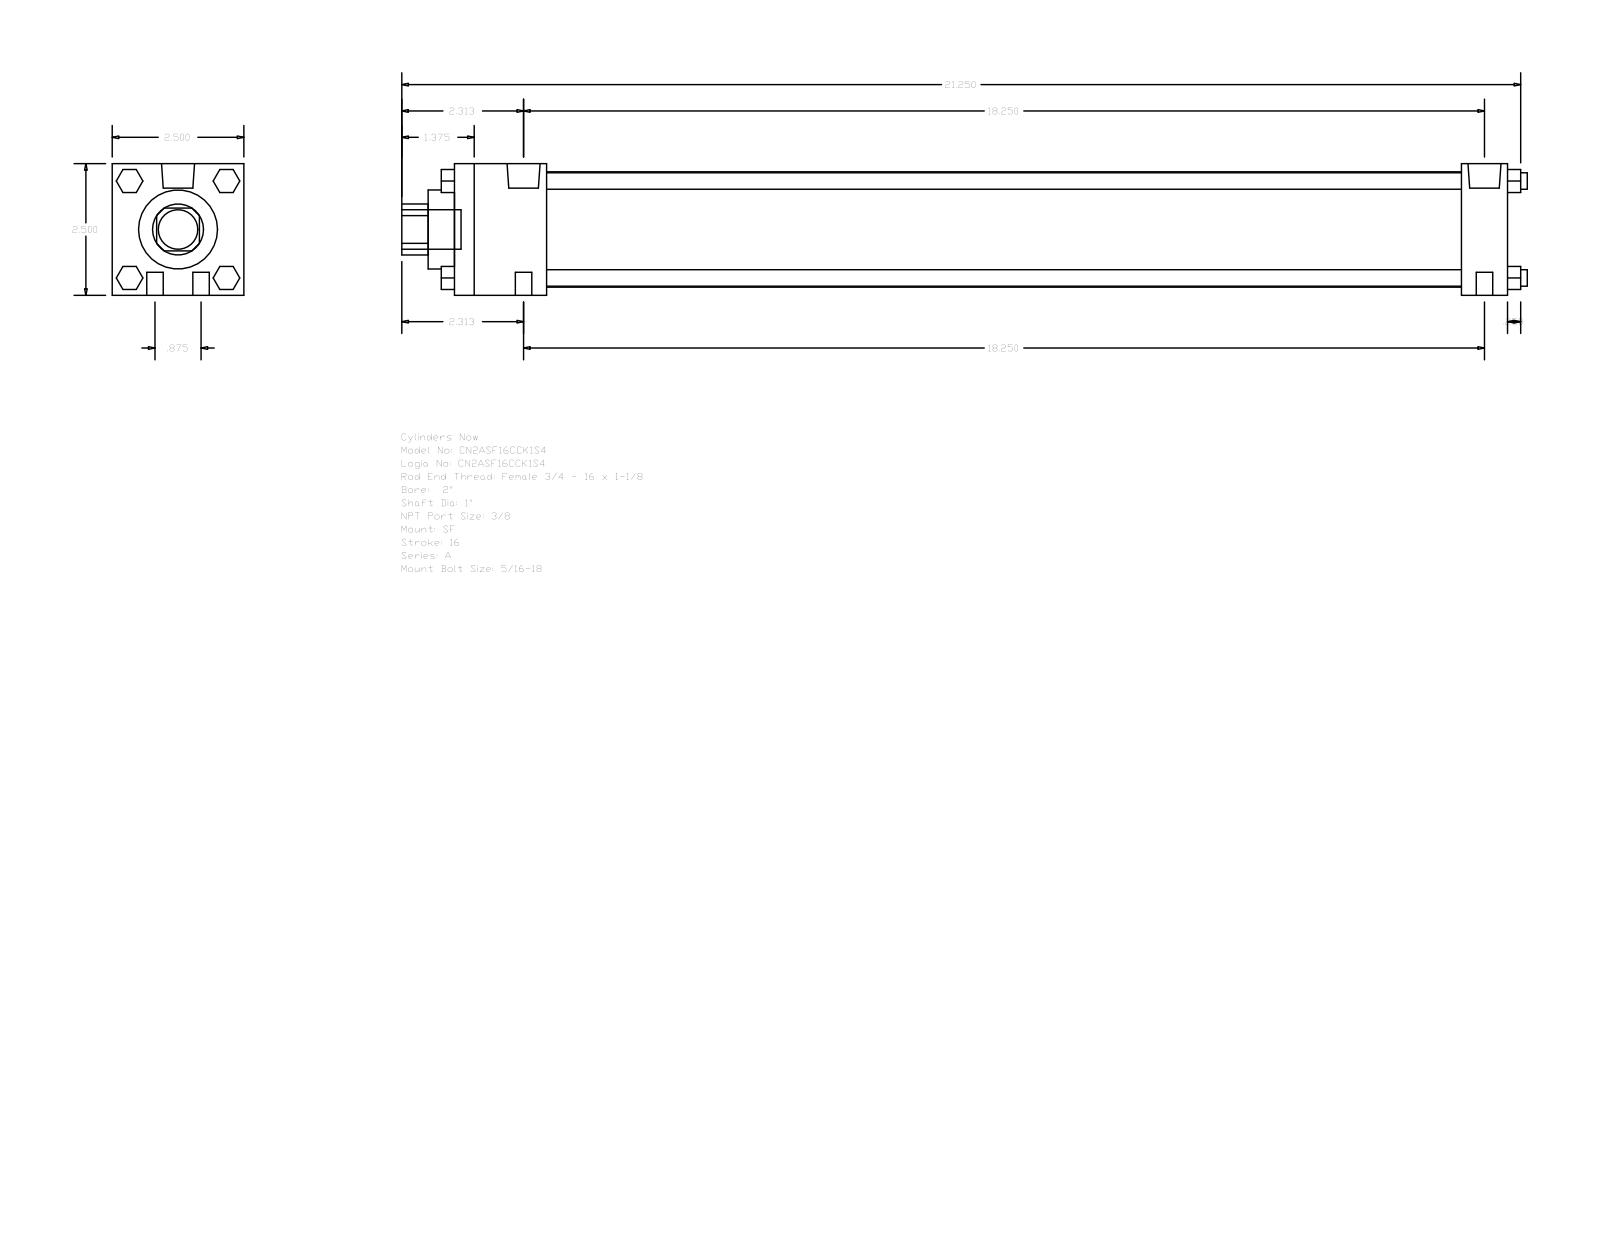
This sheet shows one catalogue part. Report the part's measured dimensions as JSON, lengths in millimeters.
{"part_name": "A_SF__0200_1", "step_written_by": "GSSL Pune (CONFIG_CONTROL_DESIGN)", "units": "millimeters", "bodies": {"solids": 0, "faces": 124, "planar": 94, "cylindrical": 30, "other": 0}, "overall_size": [542.92, 63.5, 63.5], "round_holes": [[25.4, 1], [38.1, 1], [55.63, 1]], "round_bosses_or_shafts": [[7.94, 8], [15.93, 2], [5.56, 2], [19.05, 1]], "partial_cylinders_radius": [[12.29, 1]], "face_to_face_distances": [63.5, 508, 485.78, 22.22, 44.45, 441.33, 463.55, 12.7, 520.7, 6.35]}
